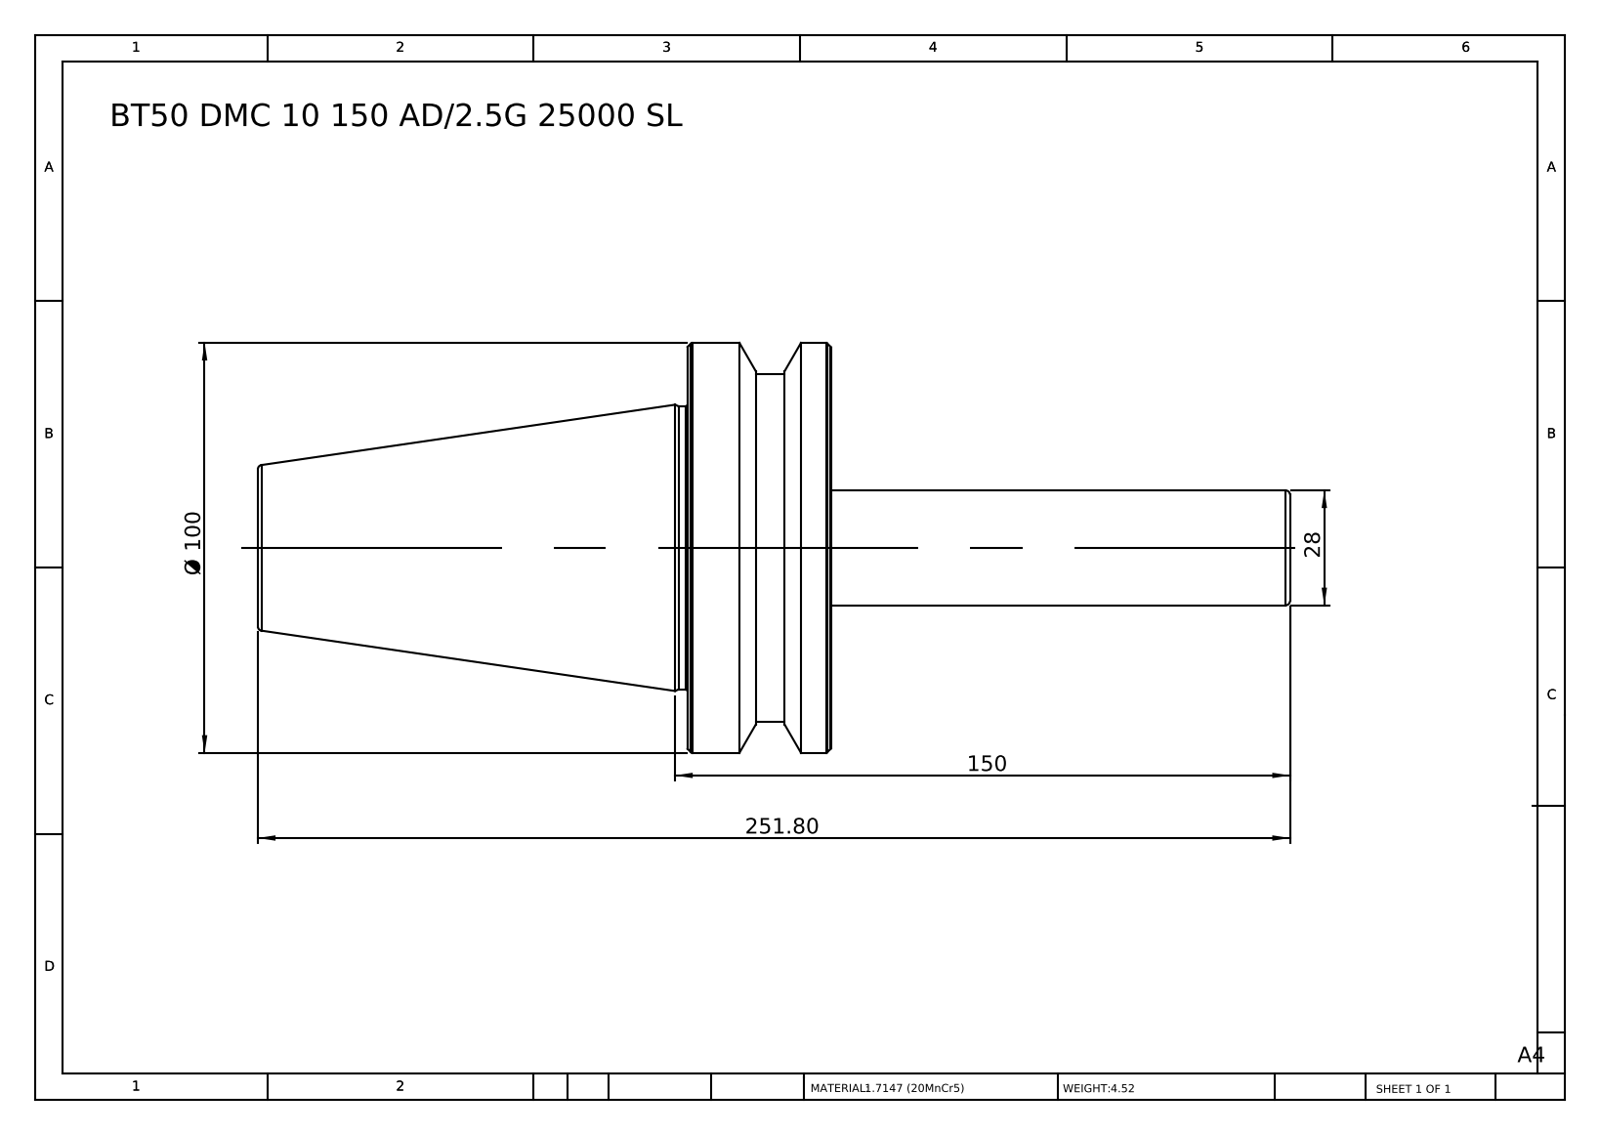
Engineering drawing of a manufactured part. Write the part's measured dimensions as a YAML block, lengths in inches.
part_name: "BT50 DMC 10 150 AD-2.5G 25000 SL"
step_written_by: "SolidWorks 2014 (CONFIG_CONTROL_DESIGN)"
units: inches
bodies: {solids: 1, faces: 42, planar: 6, cylindrical: 10, other: 26}
overall_size: [9.913, 3.937, 3.937]
volume: 35.33
surface_area: 83.95
round_bosses_or_shafts:
  - {diameter: 3.937, count: 1}
  - {diameter: 3.346, count: 1}
  - {diameter: 2.717, count: 1}
  - {diameter: 1.102, count: 1}
face_to_face_distances: [1.378, 5.504, 4.126, 4.409, 5.787, 9.913, 5.13, 0.72, 0.657, 4.783]
